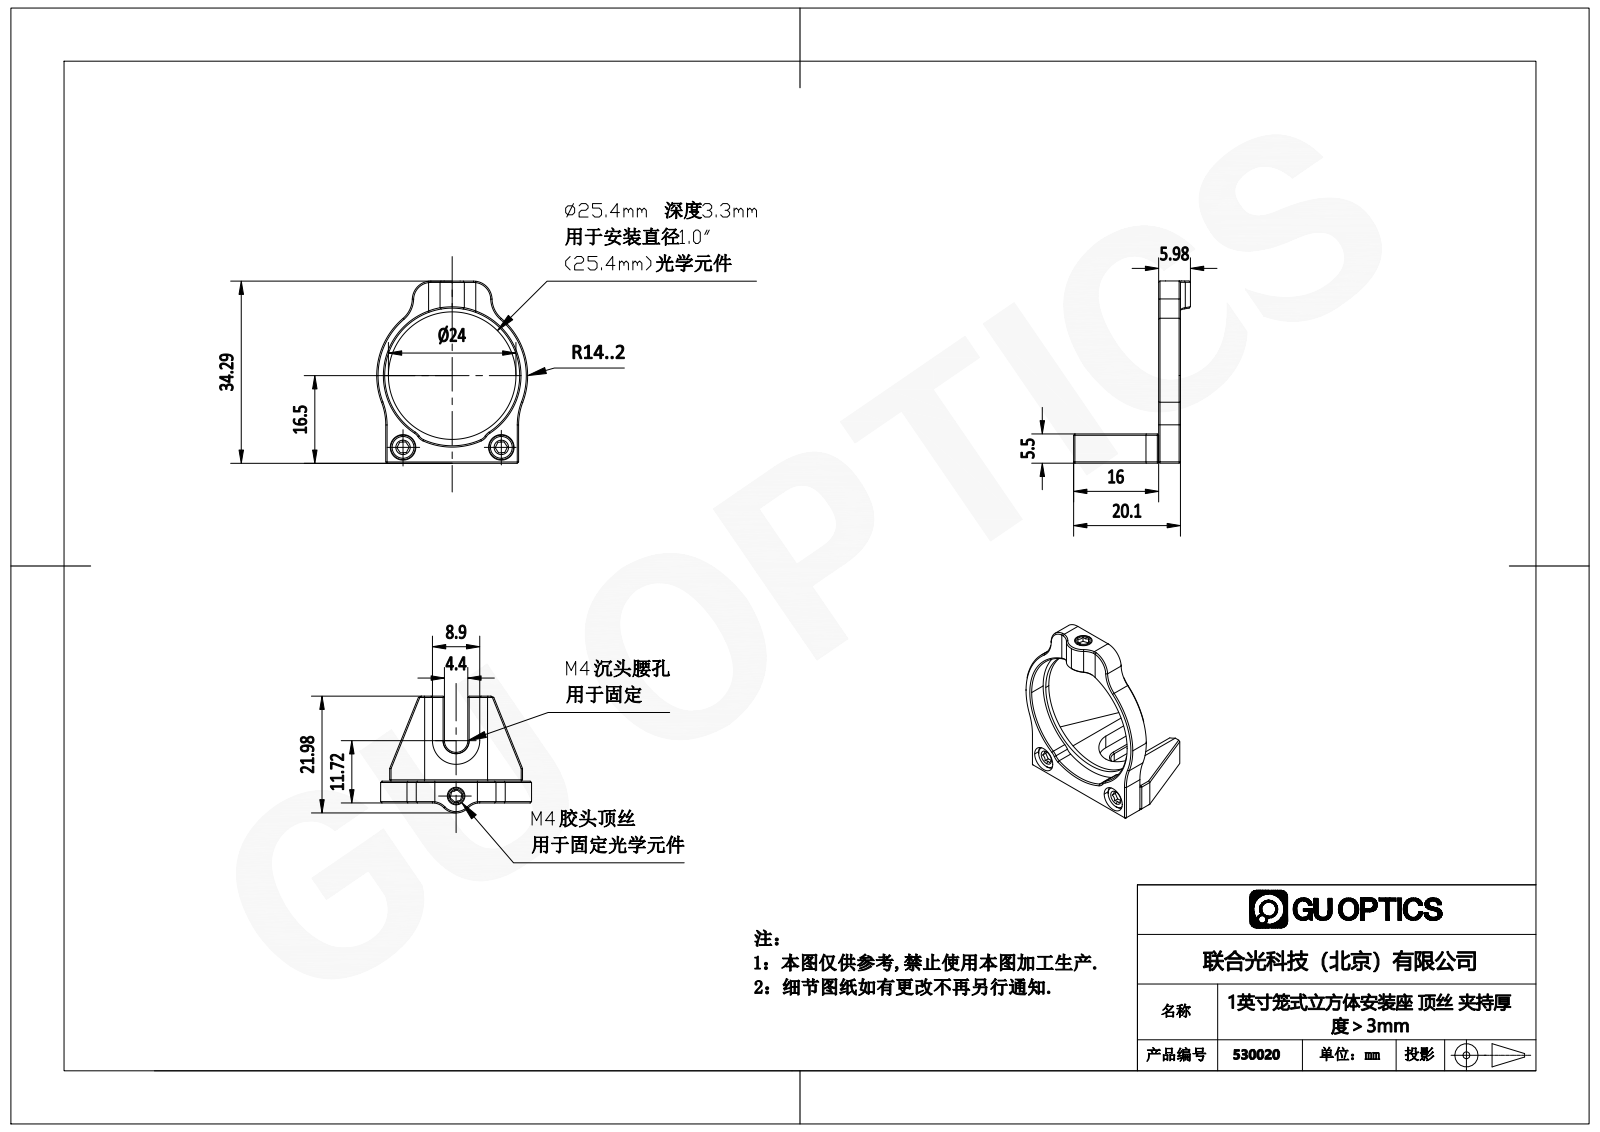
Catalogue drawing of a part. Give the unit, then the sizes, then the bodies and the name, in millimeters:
Units: millimetres
Overall size (bounding box): 34.32 × 28.4 × 21.98
Round holes (diameter × count): ⌀4.8 ×2, ⌀3.3 ×1, ⌀24 ×1, ⌀25.4 ×1
Round bosses / shafts (diameter × count): ⌀3 ×1
Partial cylindrical surfaces — rounded edges, fillets, slot ends (radius × count): R2 ×2, R2.5 ×2, R3 ×2, R3.5 ×2, R5 ×2, R12 ×2, R2.2 ×1, R3.18 ×1
Main face-to-face distances: 4.1, 5.5, 0.8, 3.3, 2.16, 3.34, 8.05, 16.95, 25, 34.29
Hole centre spacings: 16.36, 18.5
Bodies: 0 solids, 186 faces (98 planar, 36 cylindrical, 52 other)
STEP written by: SolidWorks 2018 (AUTOMOTIVE_DESIGN)
